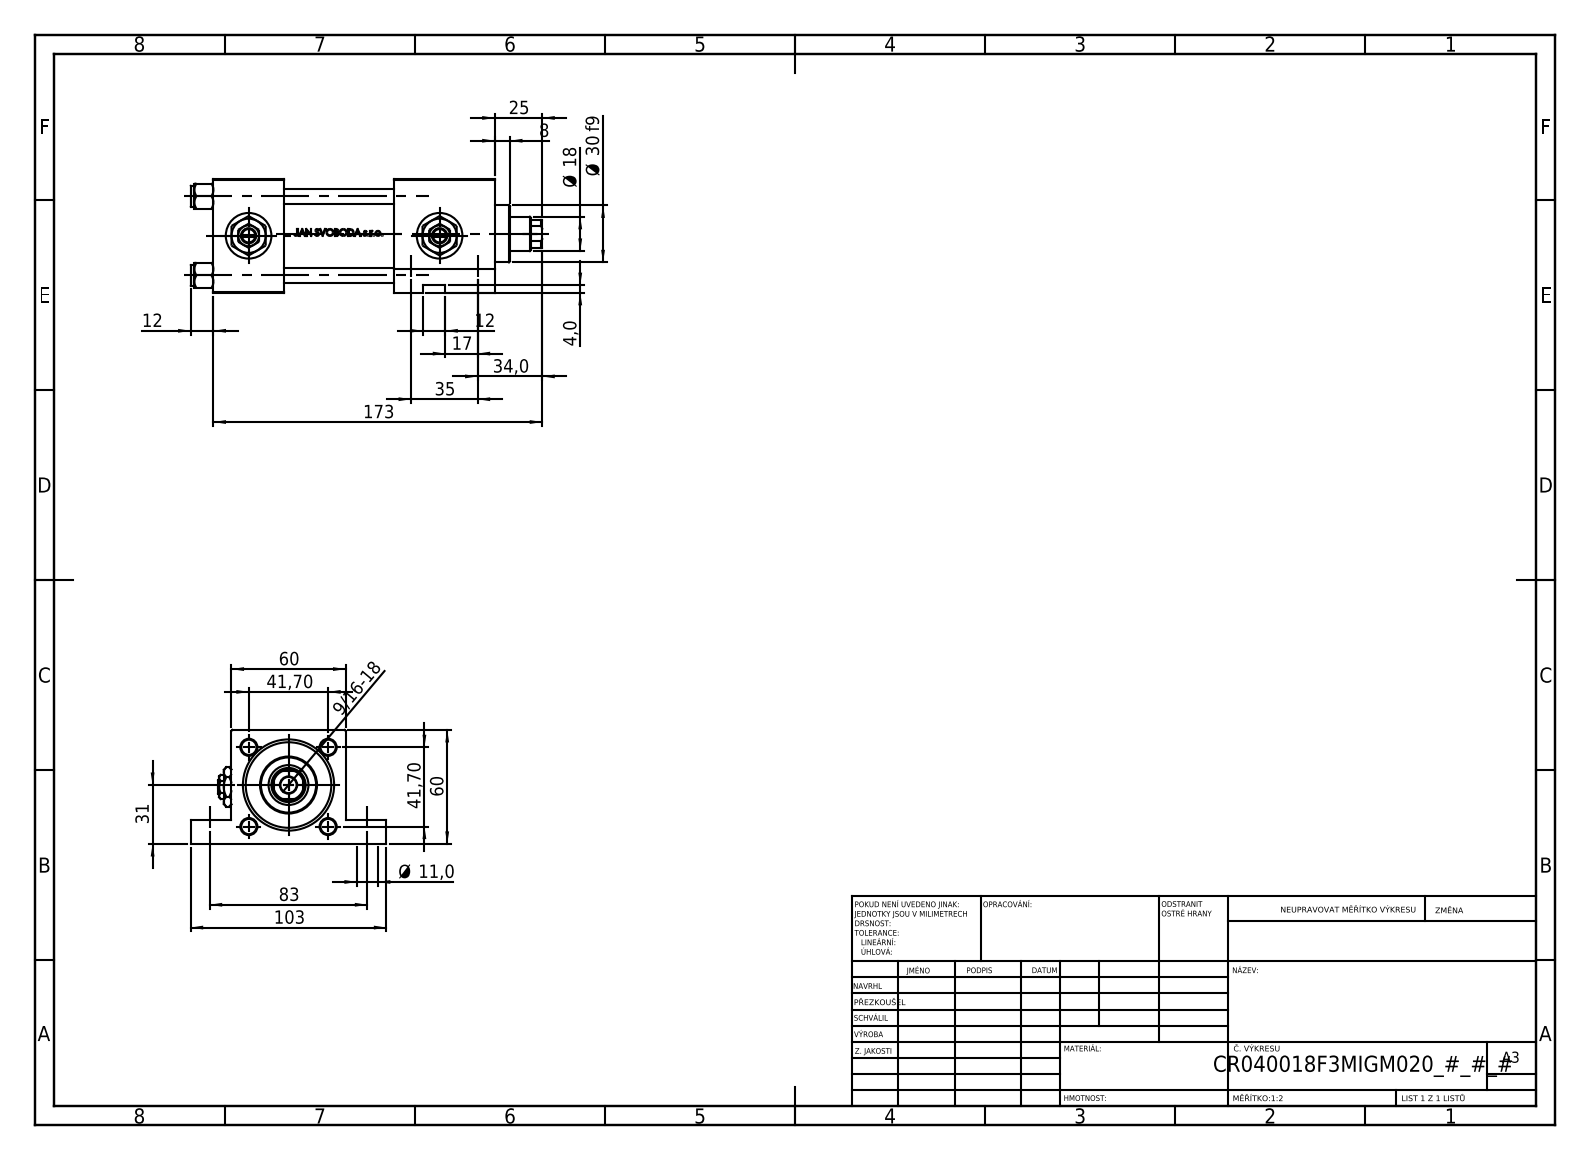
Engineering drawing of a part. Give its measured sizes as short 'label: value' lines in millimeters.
name: V215CR_F_Body; V215CR_VCP_F; V215CR_F_TYCINKA; NUT_M5_F (+2 more)
written by: SolidWorks 2019 (CONFIG_CONTROL_DESIGN)
unit: mm
bodies: 13 solids, 1215 faces (484 planar, 149 cylindrical, 582 other)
size: 185 × 103 × 60
volume: 420 373 mm³; area: 114 469 mm²
holes: 4× ⌀8, 3× ⌀16.66, 3× ⌀24, 2× ⌀7, 2× ⌀11, 2× ⌀11, 1× ⌀8.5, 1× ⌀16, 1× ⌀18, 1× ⌀21, 1× ⌀31, 1× ⌀40
bosses: 4× ⌀11, 1× ⌀46, 1× ⌀30
rounds: 1× R8.5
face distances: 60, 37, 148, 111, 53, 58, 95, 119.3, 82.3, 24.3
hole spacings: 41.7, 28.79, 30.2, 35, 42.09, 50.06, 58.97, 83
